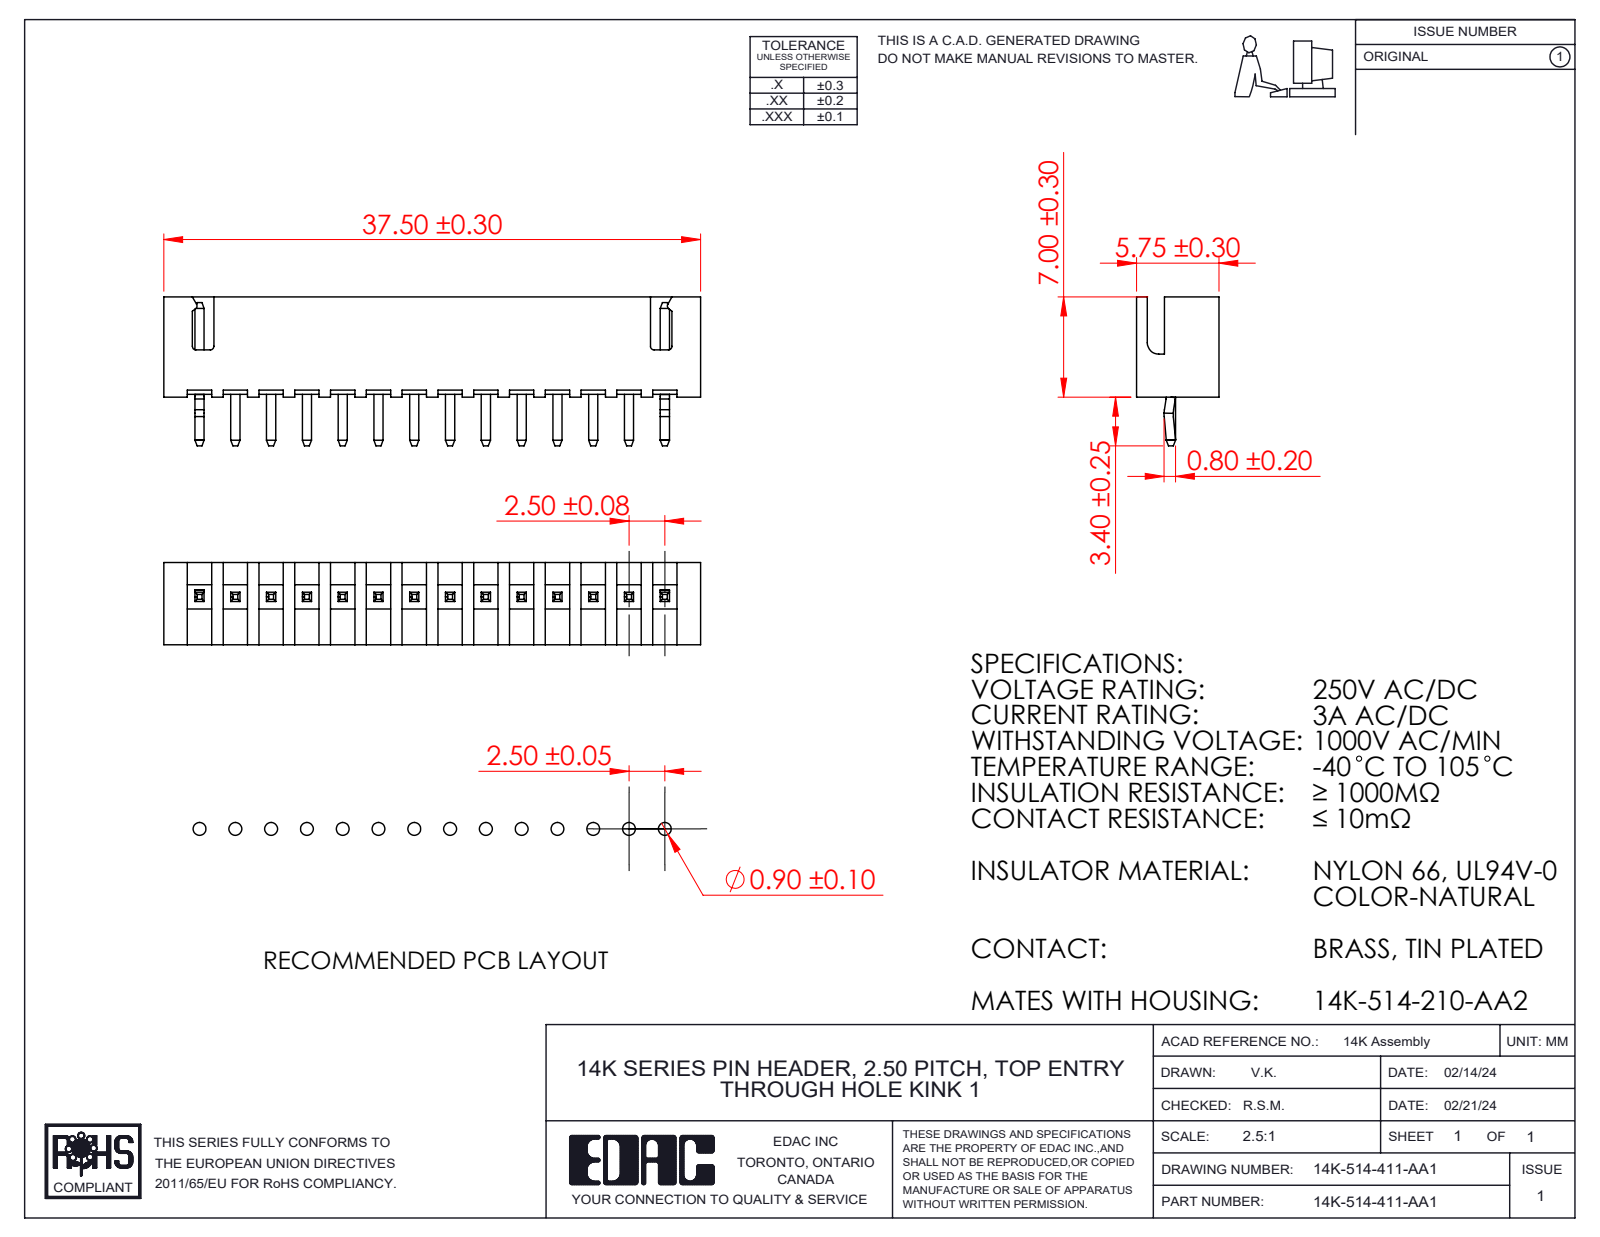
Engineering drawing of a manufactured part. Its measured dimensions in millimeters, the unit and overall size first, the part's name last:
Units: millimetres
Overall size (bounding box): 37.5 × 10.4 × 5.75
Partial cylindrical surfaces — rounded edges, fillets, slot ends (radius × count): R0.25 ×6, R2 ×4, R0.8 ×1
Main face-to-face distances: 5, 0.76, 5.76, 4.24, 0.64, 2.5, 3.04, 2.28, 1.96, 2.72
Volume: 692 mm³ · Surface area: 1 883 mm²
Bodies: 15 solids, 440 faces (419 planar, 21 cylindrical, 0 other)
Part name (STEP PRODUCT): 14K-514-411-AA1; 14K Series Pin_11; 14K Series Pin Header Insulator_514; 14K Series Pin_15
STEP written by: SolidWorks 2023 (CONFIG_CONTROL_DESIGN)
